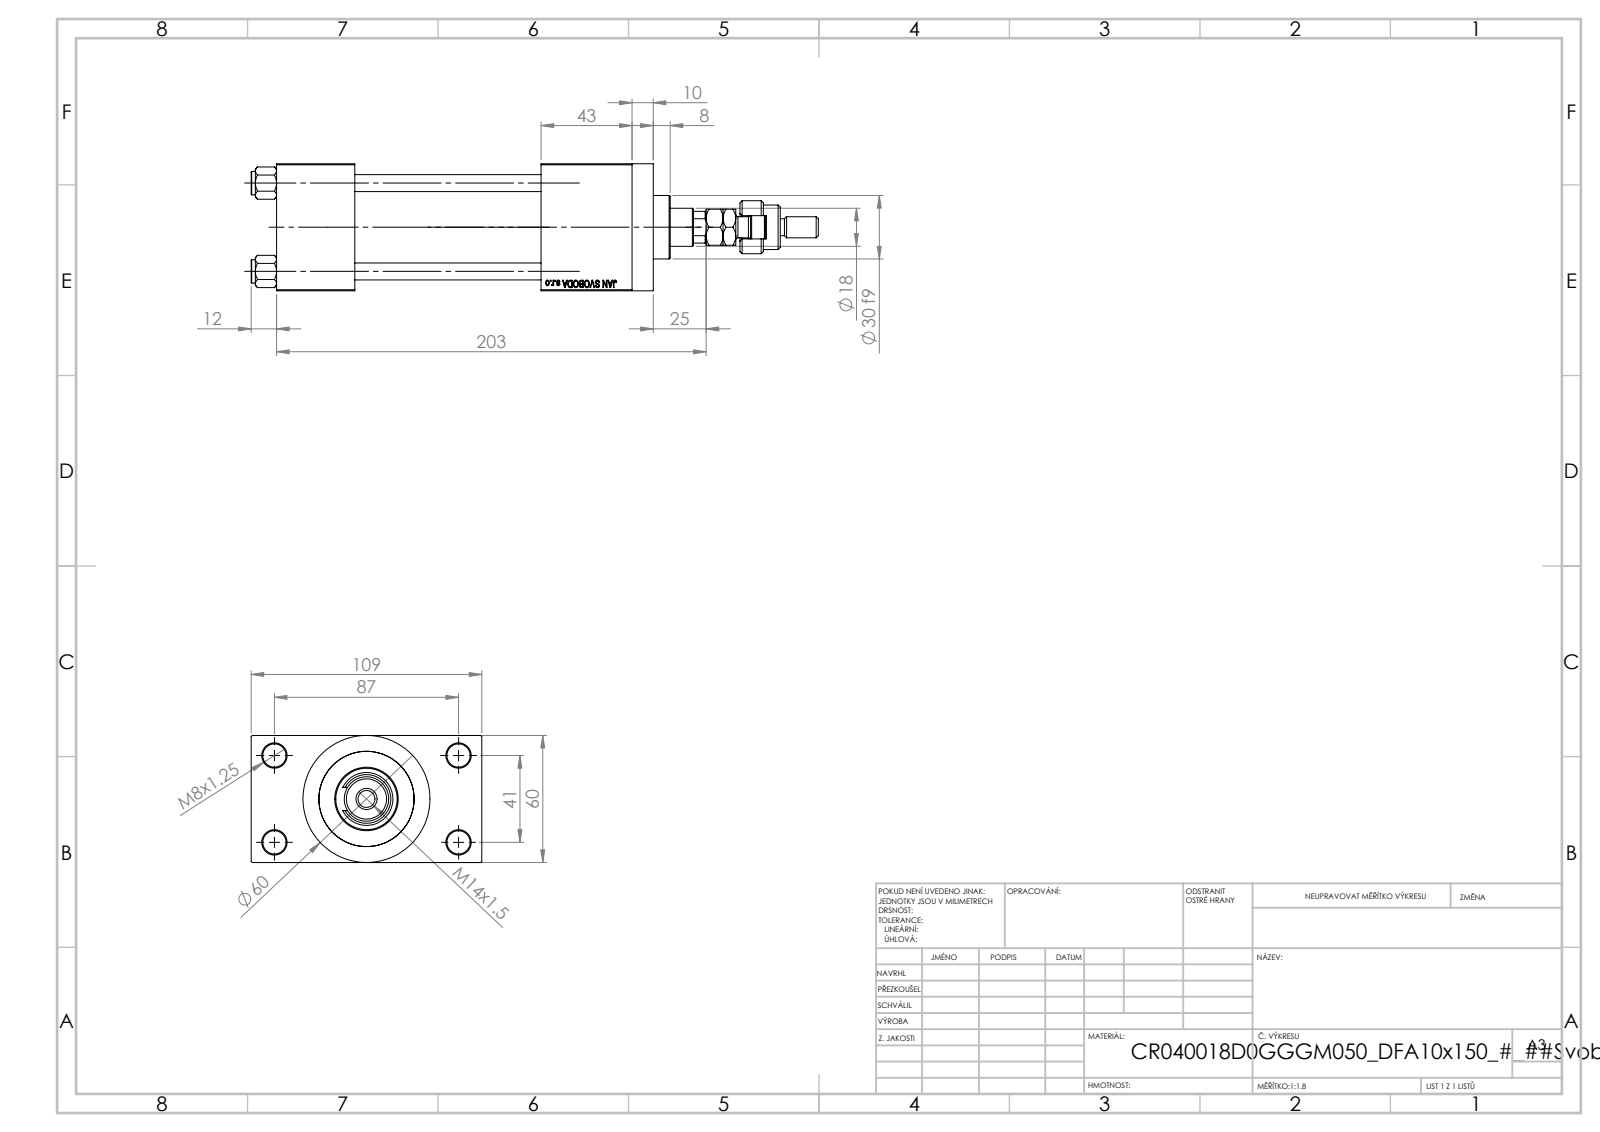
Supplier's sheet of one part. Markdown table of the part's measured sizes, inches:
| quantity | value |
| --- | --- |
| part name | NUT_M5_D; V215CR_D_TYCINKA; FEMALE_PART_FOR_DFA; V215CR_D_Body (+3 more) |
| STEP written by | SolidWorks 2019 (CONFIG_CONTROL_DESIGN) |
| units | inches |
| bodies | 13 solids, 1190 faces (526 planar, 102 cylindrical, 562 other) |
| overall size | 10.551 × 4.291 × 2.362 |
| volume | 33.89 in³ |
| surface area | 216.3 in² |
| round holes (diameter × count) | 0.315 × 4, 0.433 × 4, 0.276 × 2, 0.656 × 2, 0.945 × 2, 0.335 × 1, 0.709 × 1, 0.827 × 1, 1.22 × 1, 1.575 × 1, 1.772 × 1 |
| round bosses / shafts (diameter × count) | 0.433 × 4, 2.362 × 1, 1.811 × 1, 1.181 × 1, 0.984 × 1, 0.63 × 1, 0.394 × 1, 0.315 × 1 |
| partial cylindrical surfaces (radius × count) | 0.217 × 1, 0.335 × 1, 0.344 × 1 |
| main face-to-face distances | 2.362, 0.965, 3.327, 3.465, 1.457, 4.921, 6.614, 5.157, 1.693, 4.291 |
| hole center spacings | 0.892, 1.161, 1.642, 1.856, 1.893, 2.533, 3.011, 1.614 |
